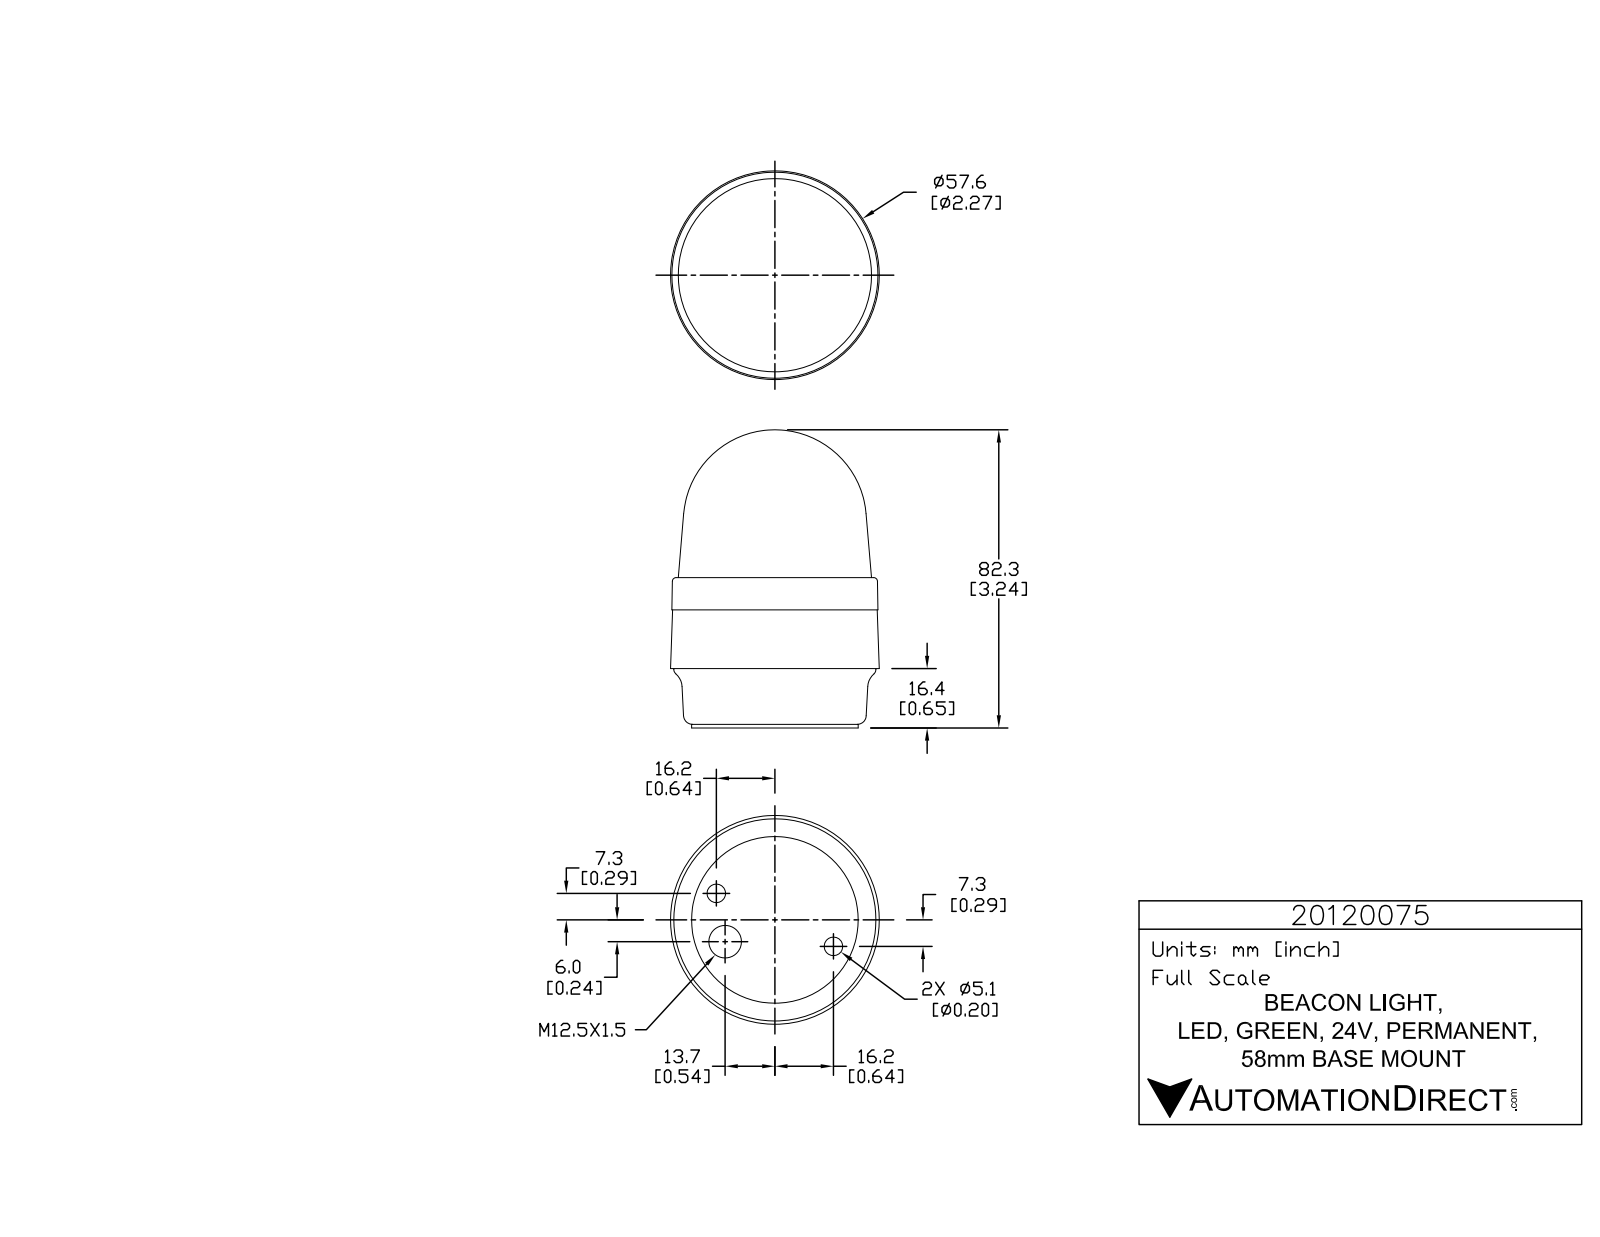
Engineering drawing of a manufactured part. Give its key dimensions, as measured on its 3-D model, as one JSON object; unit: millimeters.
{"part_name": "20120075", "step_written_by": "SolidWorks 2015 (AUTOMOTIVE_DESIGN)", "units": "millimeters", "bodies": {"solids": 1, "faces": 763, "planar": 527, "cylindrical": 145, "other": 91}, "overall_size": [82.3, 57.63, 57.63], "volume_mm3": 164395, "surface_area_mm2": 16261, "round_holes": [[0.99, 3], [5.11, 2], [9, 1]], "round_bosses_or_shafts": [[5.74, 3], [1.43, 3], [55.8, 1], [46, 1]], "partial_cylinders_radius": [[0.2, 6], [0.21, 6], [0.21, 6], [3.32, 6], [0.1, 3], [0.12, 3], [0.19, 3], [0.2, 3]], "face_to_face_distances": [16.4, 1, 15.4, 41.5, 40.5, 25.1, 32.6, 31.6, 16.2, 8.9], "hole_center_spacings": [13.56, 29.94, 35.5]}
